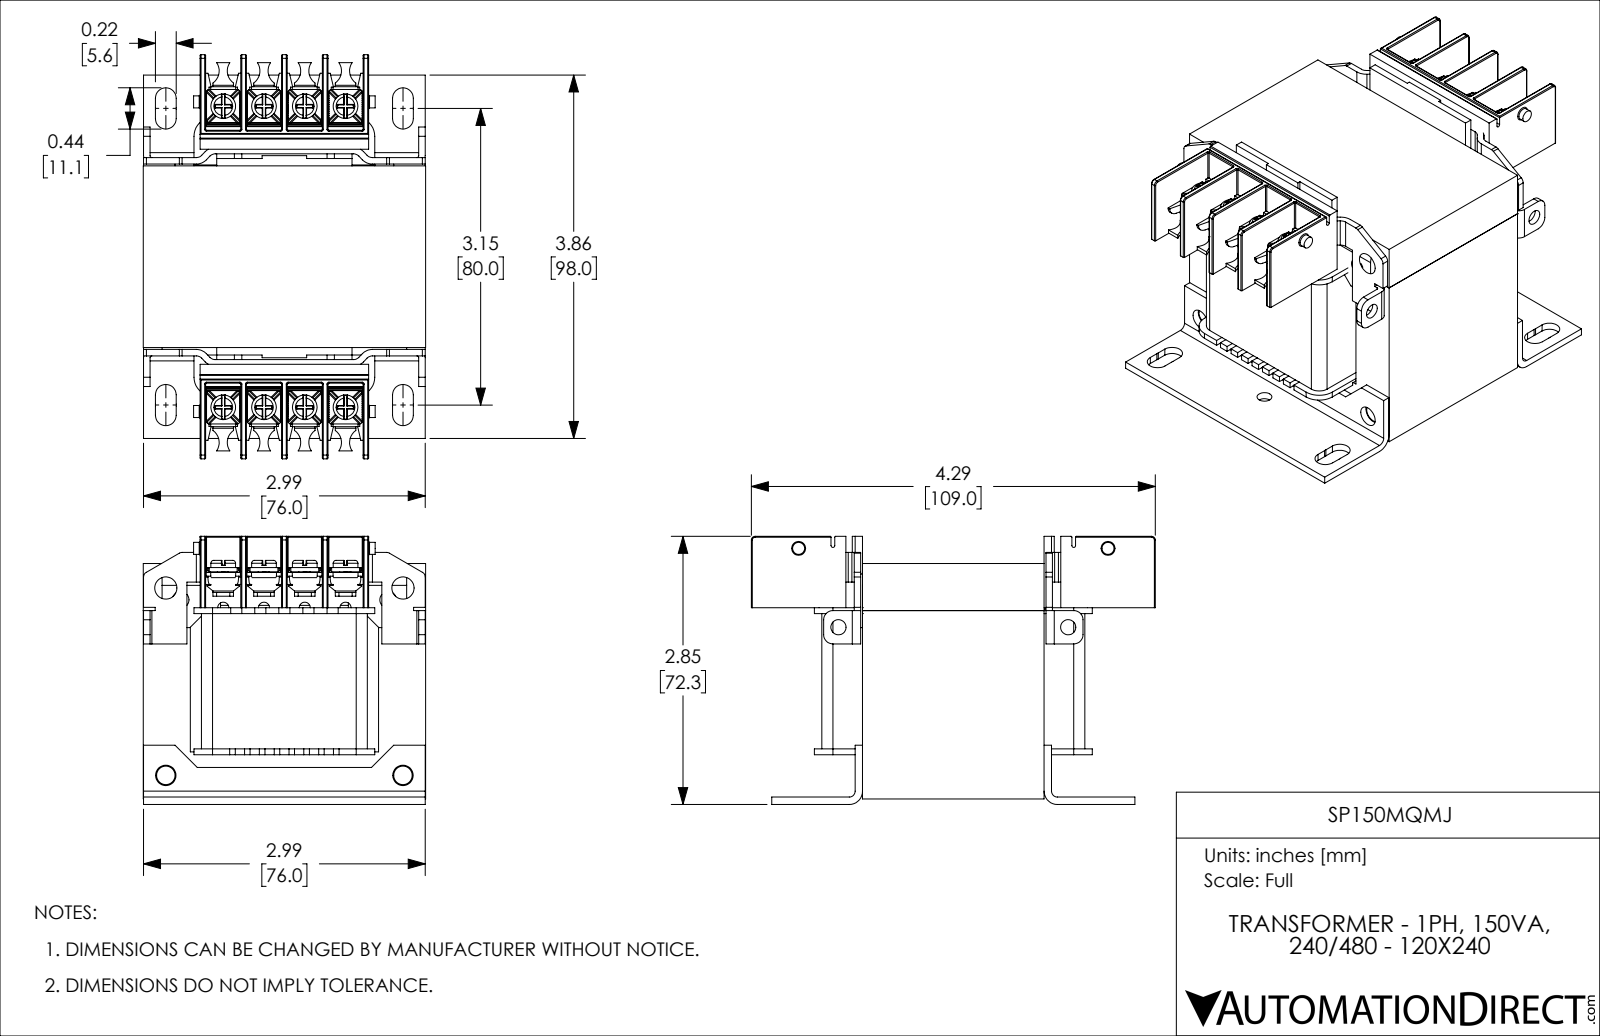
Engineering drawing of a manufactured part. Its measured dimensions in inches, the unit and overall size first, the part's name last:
Units: inches
Overall size (bounding box): 4.291 × 3 × 2.847
Round holes (diameter × count): ⌀0.157 ×10, ⌀0.105 ×8, ⌀0.138 ×8, ⌀0.1 ×2, ⌀0.161 ×2, ⌀0.177 ×2, ⌀0.197 ×2, ⌀0.217 ×2, ⌀0.236 ×2
Round bosses / shafts (diameter × count): ⌀0.262 ×8, ⌀0.24 ×8, ⌀0.168 ×8, ⌀0.11 ×8, ⌀0.128 ×3
Partial cylindrical surfaces — rounded edges, fillets, slot ends (radius × count): R0.005 ×52, R0.01 ×52, R0.012 ×46, R0.029 ×32, R0.059 ×18, R0.157 ×16, R0.035 ×12, R0.079 ×10
Main face-to-face distances: 0.5, 2, 0.059, 0.433, 0.079, 2.5, 2.382, 1, 1.929, 1.5
Hole centre spacings: 0.433, 0.866, 3.216, 1.299, 3.187, 3.303, 3.207, 3.226
Volume: 18.42 in³ · Surface area: 166 in²
Bodies: 42 solids, 3183 faces (1948 planar, 941 cylindrical, 294 other)
Part name (STEP PRODUCT): SP150MQMJ
STEP written by: SolidWorks 2018 (AUTOMOTIVE_DESIGN)
